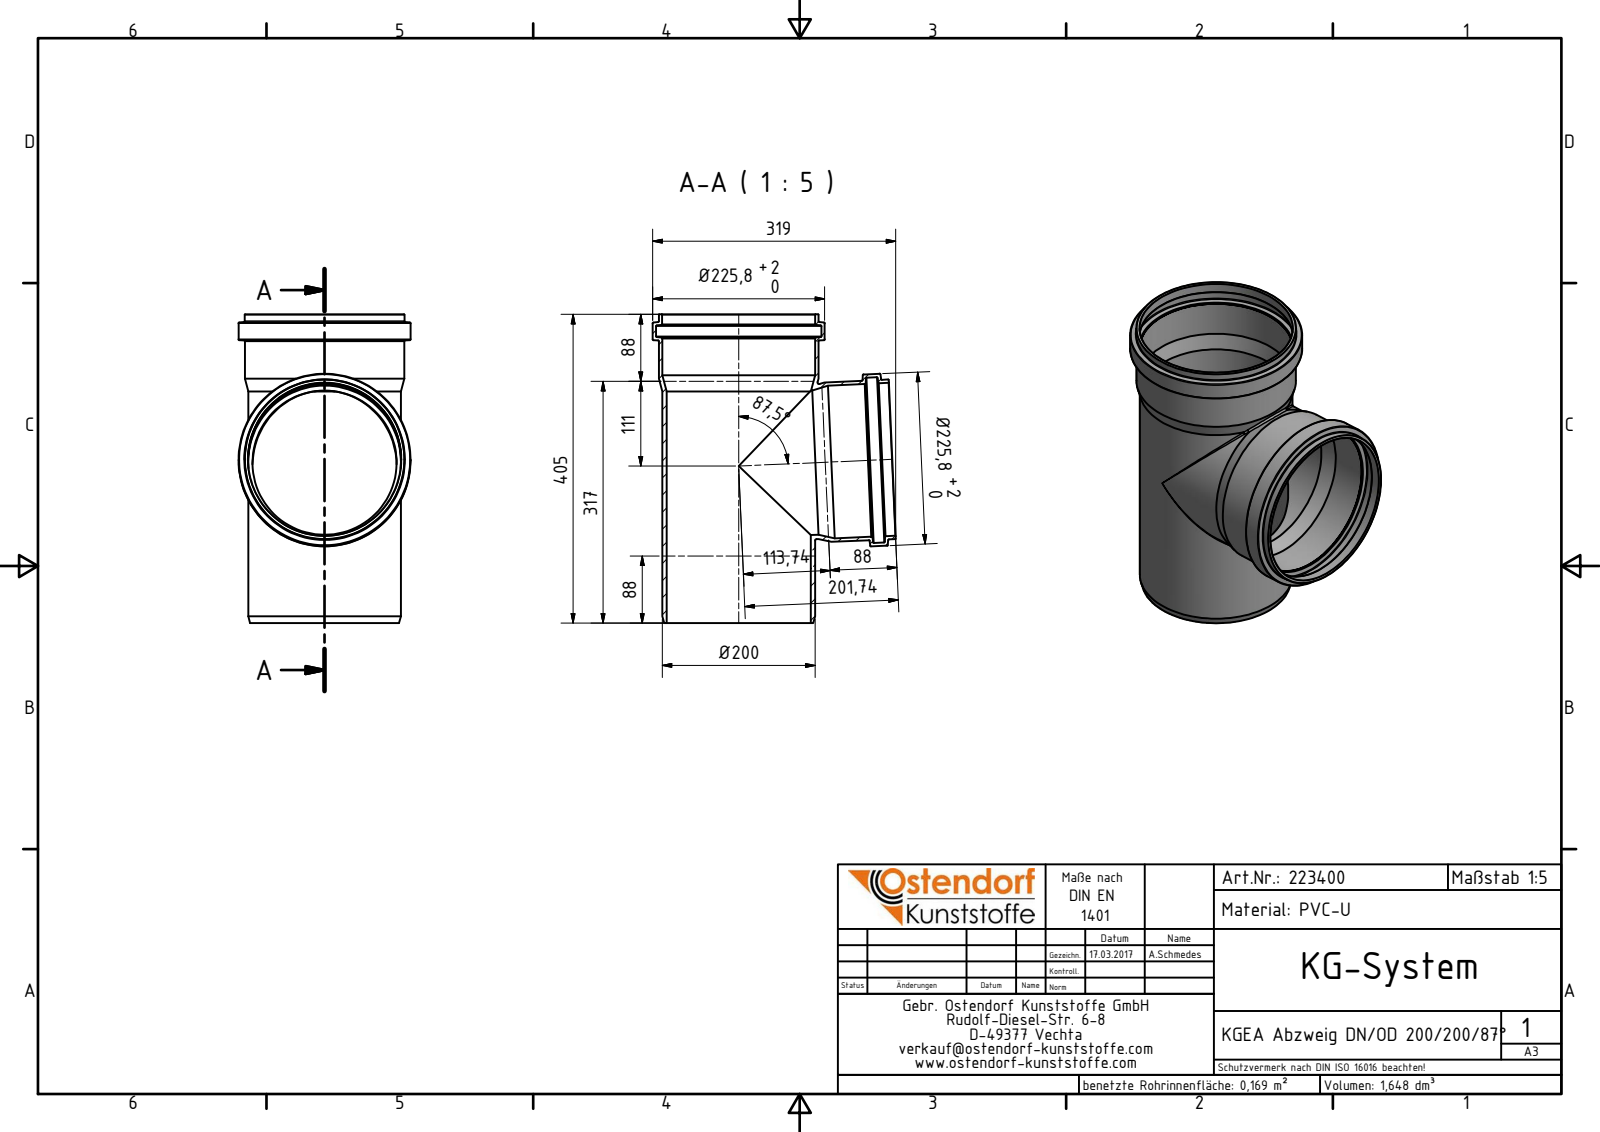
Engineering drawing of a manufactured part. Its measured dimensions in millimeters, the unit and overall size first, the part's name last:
Units: millimetres
Overall size (bounding box): 405 × 319 × 225.8
Round holes (diameter × count): ⌀200.9 ×3, ⌀189.3 ×2, ⌀200.6 ×2, ⌀217 ×2
Round bosses / shafts (diameter × count): ⌀225.8 ×2, ⌀209.7 ×2, ⌀209.4 ×2, ⌀200.5 ×2
Main face-to-face distances: 405, 31.77, 373.23
Volume: 1 648 000 mm³ · Surface area: 650 462 mm²
Bodies: 1 solid, 62 faces (5 planar, 18 cylindrical, 39 other)
Part name (STEP PRODUCT): 223400 KGEA Abzweig DN_OD 200_200_87°
STEP written by: Autodesk Inventor 2016 (AUTOMOTIVE_DESIGN)
